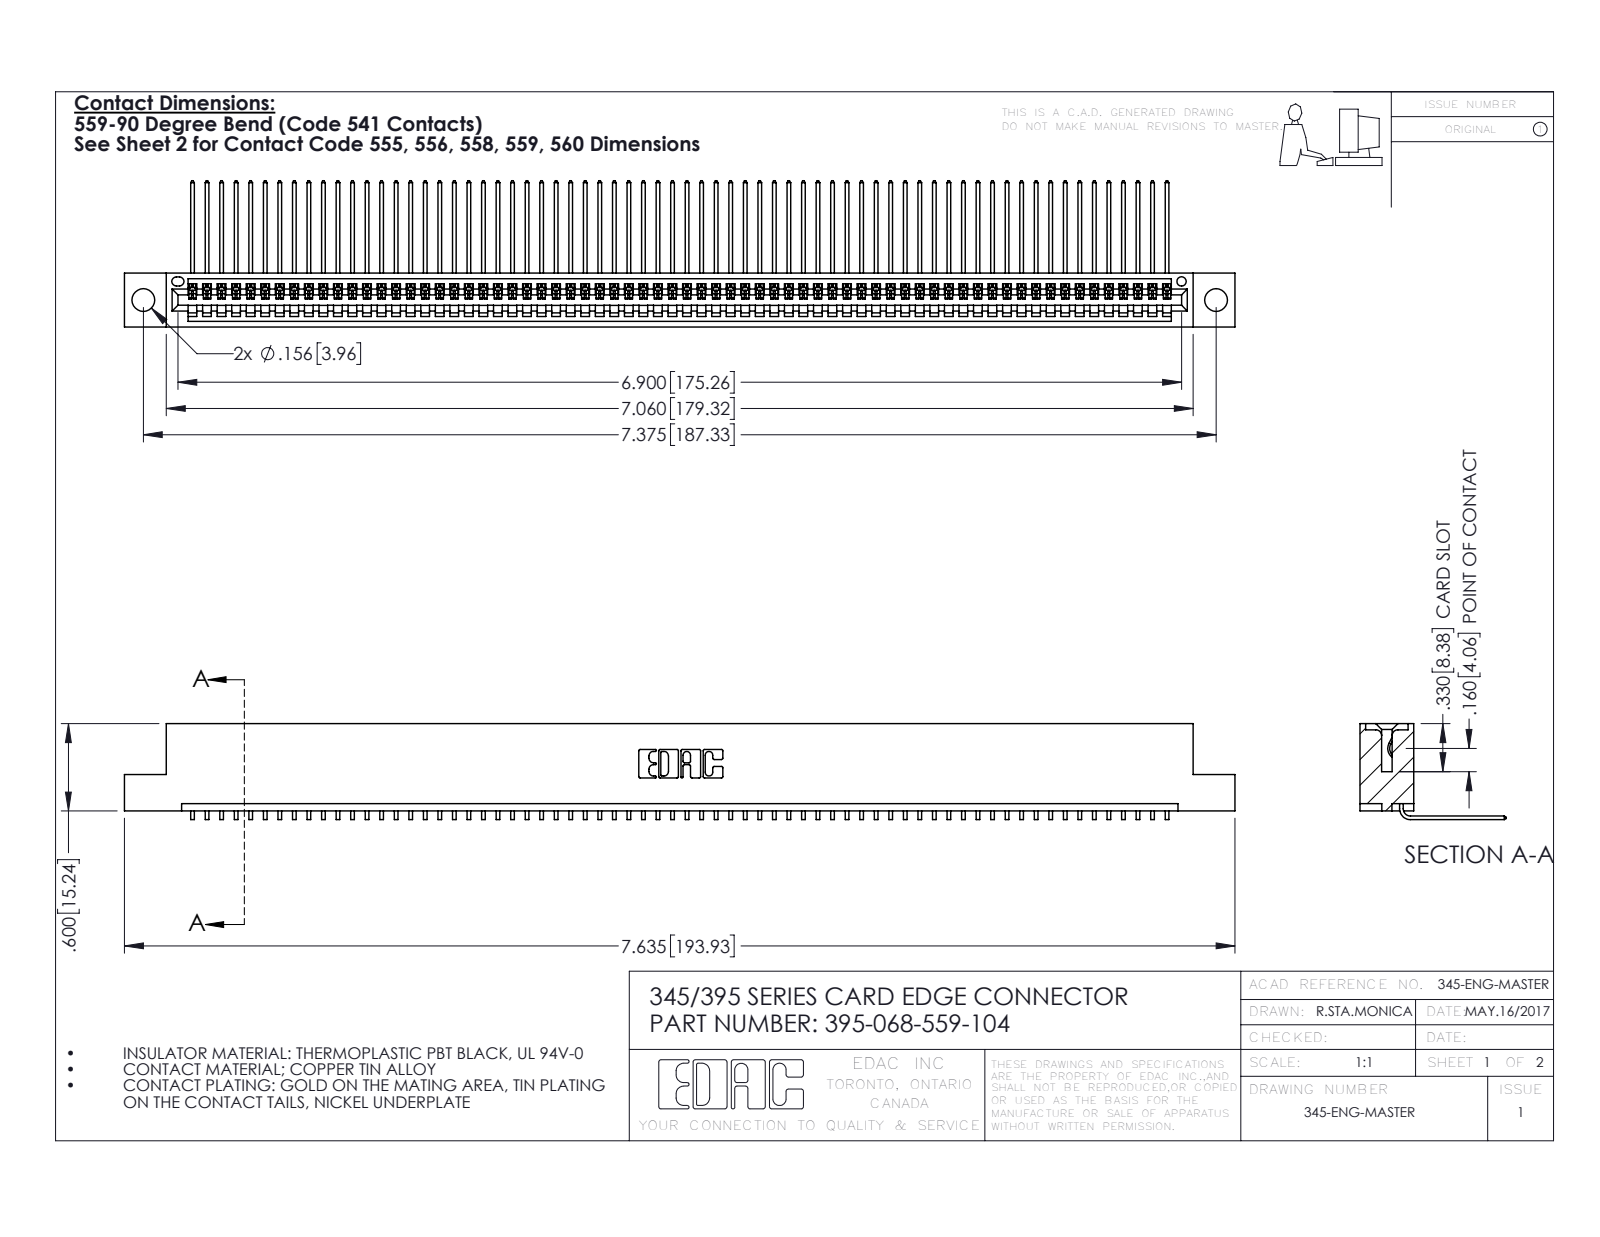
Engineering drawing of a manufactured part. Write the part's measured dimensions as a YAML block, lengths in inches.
part_name: "345-292-001_558 559 Tail - 1; 395-068-559-104; 345 Part_Flush Mounting Lugs - 0.156 Dia-TH"
step_written_by: "SolidWorks 2016 (CONFIG_CONTROL_DESIGN)"
units: inches
bodies: {solids: 69, faces: 4206, planar: 2936, cylindrical: 1270, other: 0}
overall_size: [7.635, 1.005, 0.659]
volume: 1.145
surface_area: 40.98
round_holes:
  - {diameter: 0.156, count: 2}
  - {diameter: 0.064, count: 1}
partial_cylinders:
  - {radius: 0.006, count: 136}
  - {radius: 0.01, count: 22}
  - {radius: 0.007, count: 6}
  - {radius: 0.031, count: 6}
  - {radius: 0.026, count: 3}
  - {radius: 0.031, count: 2}
  - {radius: 0.04, count: 2}
  - {radius: 0.014, count: 1}
face_to_face_distances: [0.298, 0.072, 0.37, 0.2, 0.098, 0.272, 0.025, 0.225, 0.149, 0.072]
hole_center_spacings: [0.27, 7.139, 7.375]
